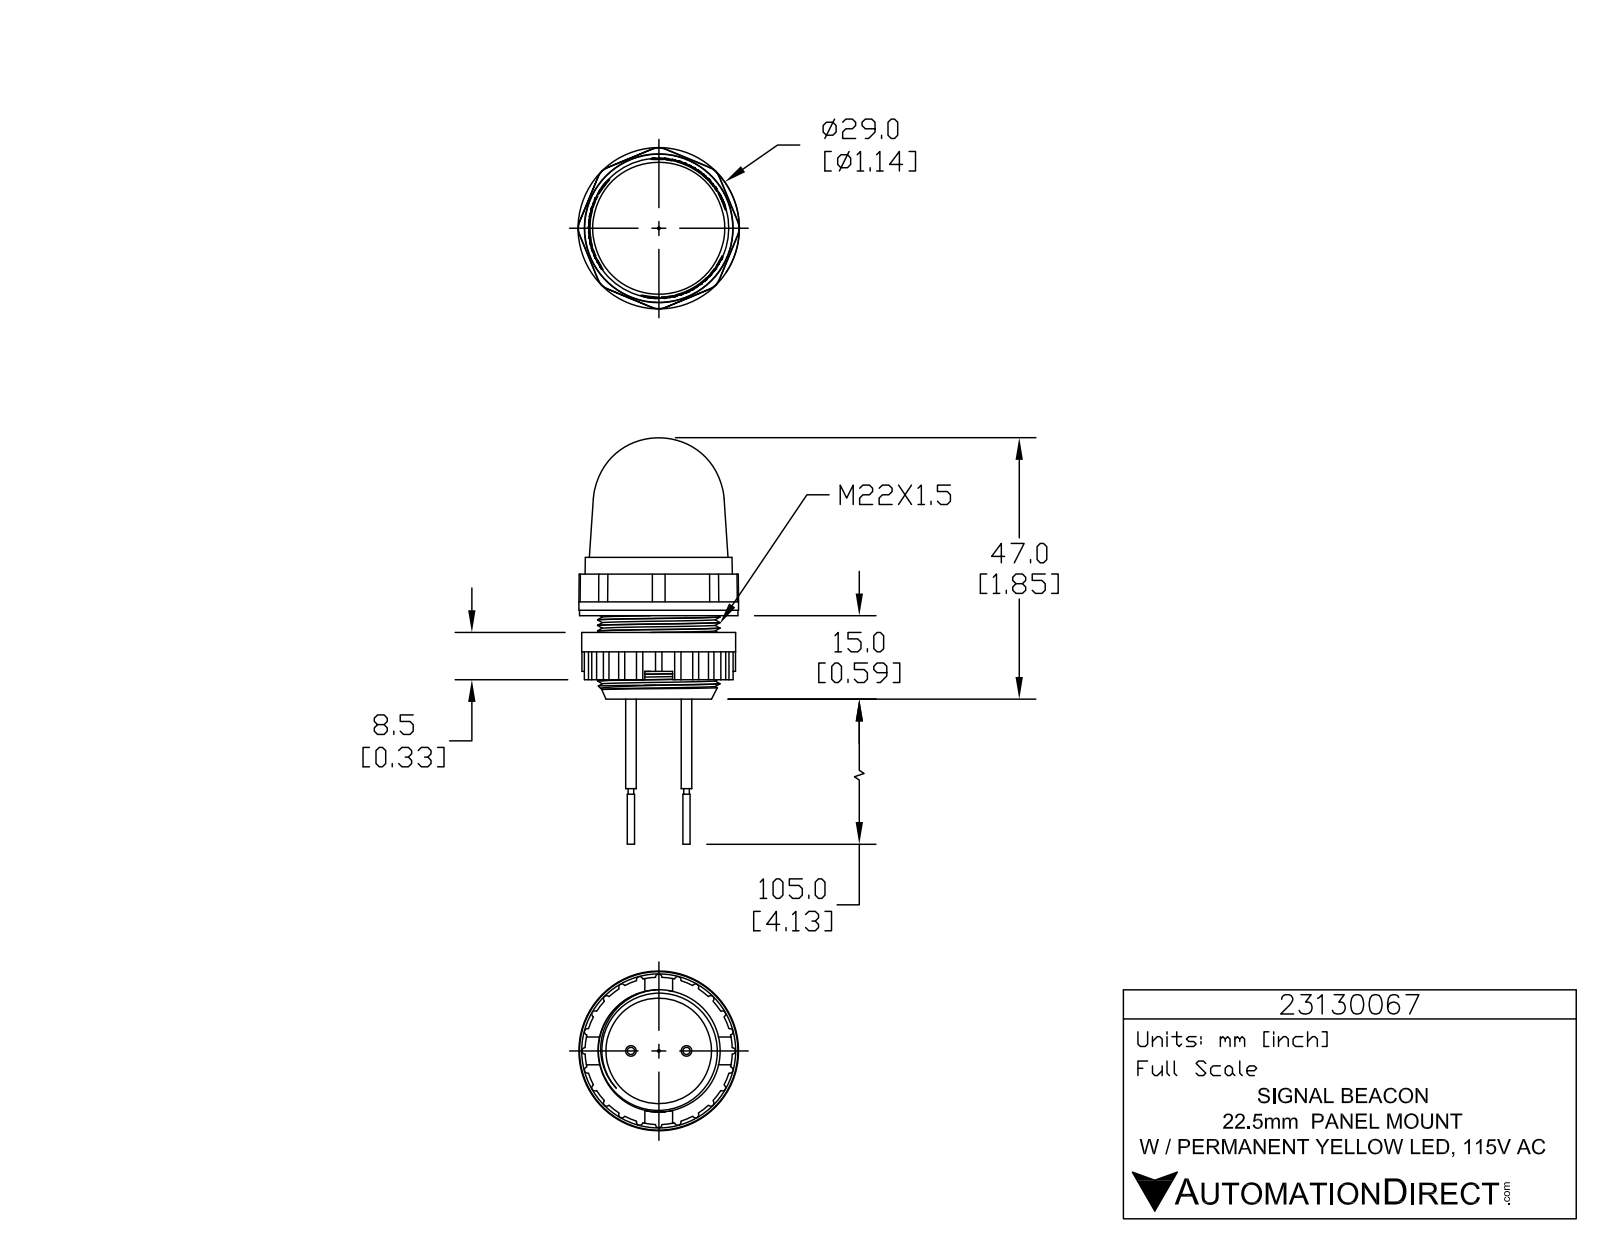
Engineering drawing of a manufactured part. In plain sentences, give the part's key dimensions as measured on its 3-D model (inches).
The part is named "23130067". Its 3-D file was written by "SolidWorks 2017 (AUTOMOTIVE_DESIGN)". It is 1 solid with 934 faces: 568 planar, 269 cylindrical and 97 other. Overall it measures 2.82 by 1.131 by 1.131 inches. Its volume is 1.255 cubic inches and its surface area 12.16 square inches. Round holes: 3 of diameter 0.02. Round bosses or shafts: 3 of diameter 0.113, 3 of diameter 0.028, 2 of diameter 0.075, 2 of diameter 0.051, 2 of diameter 0.039, 1 of diameter 1.131, 1 of diameter 1.122, 1 of diameter 1.091. Partial cylindrical surfaces (rounded edges, fillets, slot ends): 24 of radius 0.023, 8 of radius 0.118, 6 of radius 0.004, 6 of radius 0.004, 6 of radius 0.004, 6 of radius 0.065, 3 of radius 0.005, 3 of radius 0.007. The main face-to-face distances are 0.551, 0.118, 0.433, 0.098, 0.335, 0.453, 0.492, 0.413, 0.295, 0.197.
